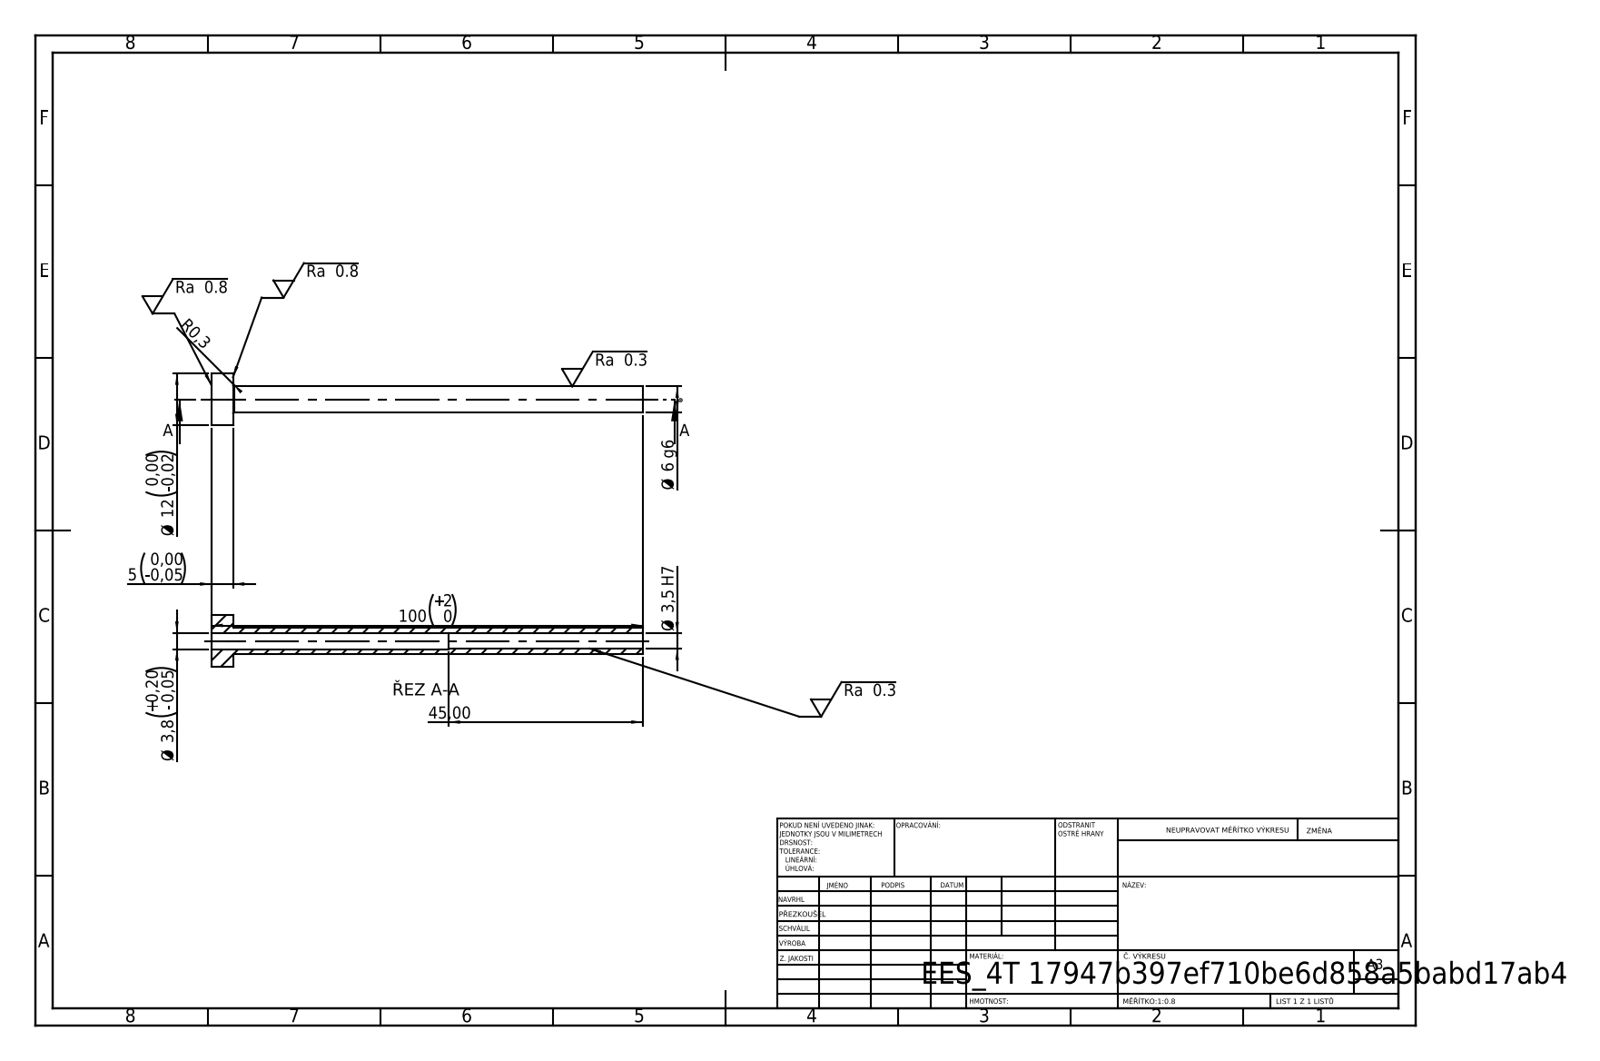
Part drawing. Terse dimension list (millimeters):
written by: SolidWorks 2019 (CONFIG_CONTROL_DESIGN)
unit: mm
bodies: 1 solid, 14 faces (4 planar, 8 cylindrical, 2 other)
size: 100 × 12 × 12
volume: 2 195 mm³; area: 3 335 mm²
holes: 1× ⌀3.5, 1× ⌀3.8
bosses: 1× ⌀12, 1× ⌀6
face distances: 5, 100, 95, 55, 50, 45
